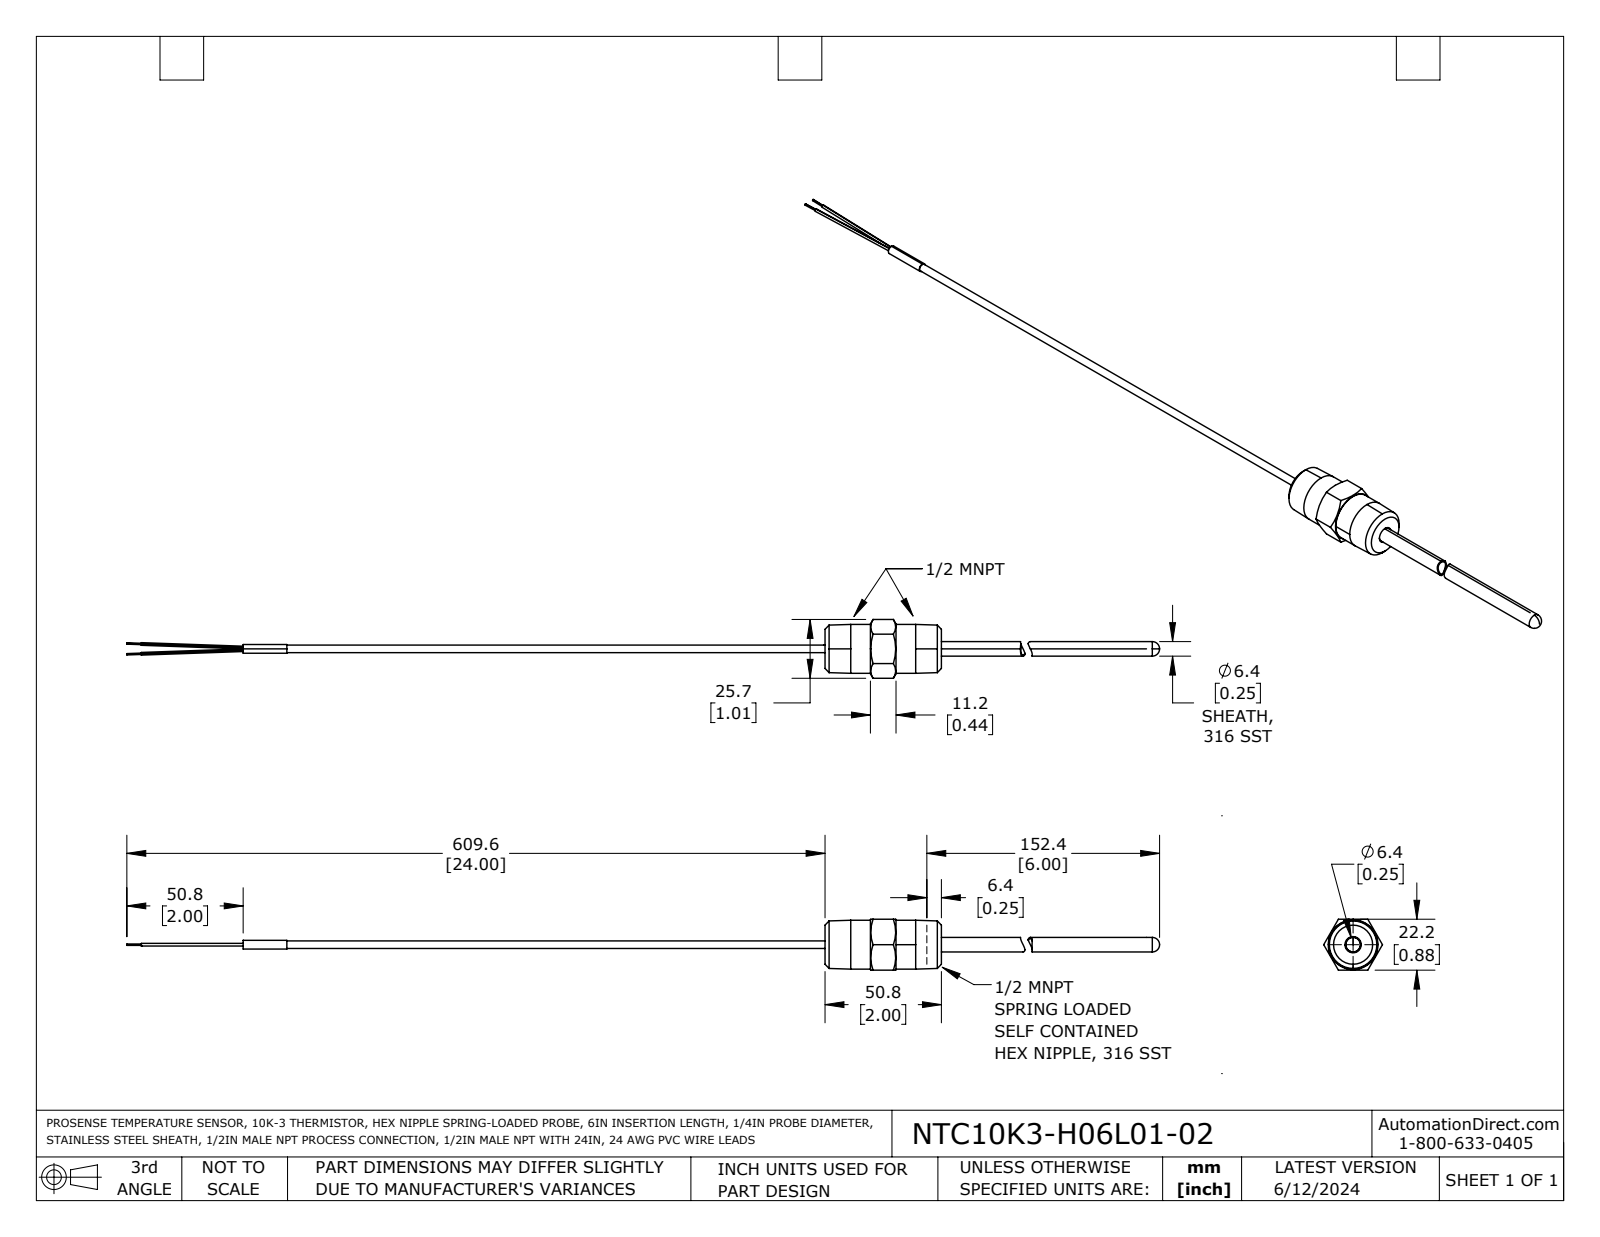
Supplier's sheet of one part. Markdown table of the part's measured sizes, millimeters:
| quantity | value |
| --- | --- |
| part name | NTC10K3-H06L01-02 |
| STEP written by | SolidWorks 2021 (AUTOMOTIVE_DESIGN) |
| units | millimeters |
| bodies | 2 solids, 74 faces (24 planar, 22 cylindrical, 28 other) |
| overall size | 501.5 × 25.7 × 22.2 |
| volume | 17 960 mm³ |
| surface area | 14 820 mm² |
| round holes (diameter × count) | 3.3 × 1, 5.3 × 1, 6.6 × 1, 11.1 × 1, 11.8 × 1 |
| round bosses / shafts (diameter × count) | 21.3 × 1, 11.6 × 1, 6.4 × 1, 3.8 × 1, 3.3 × 1 |
| main face-to-face distances | 22.2, 50.8, 2.7, 48.1, 2.5, 50.6, 19.8, 31, 191.1, 191 |
